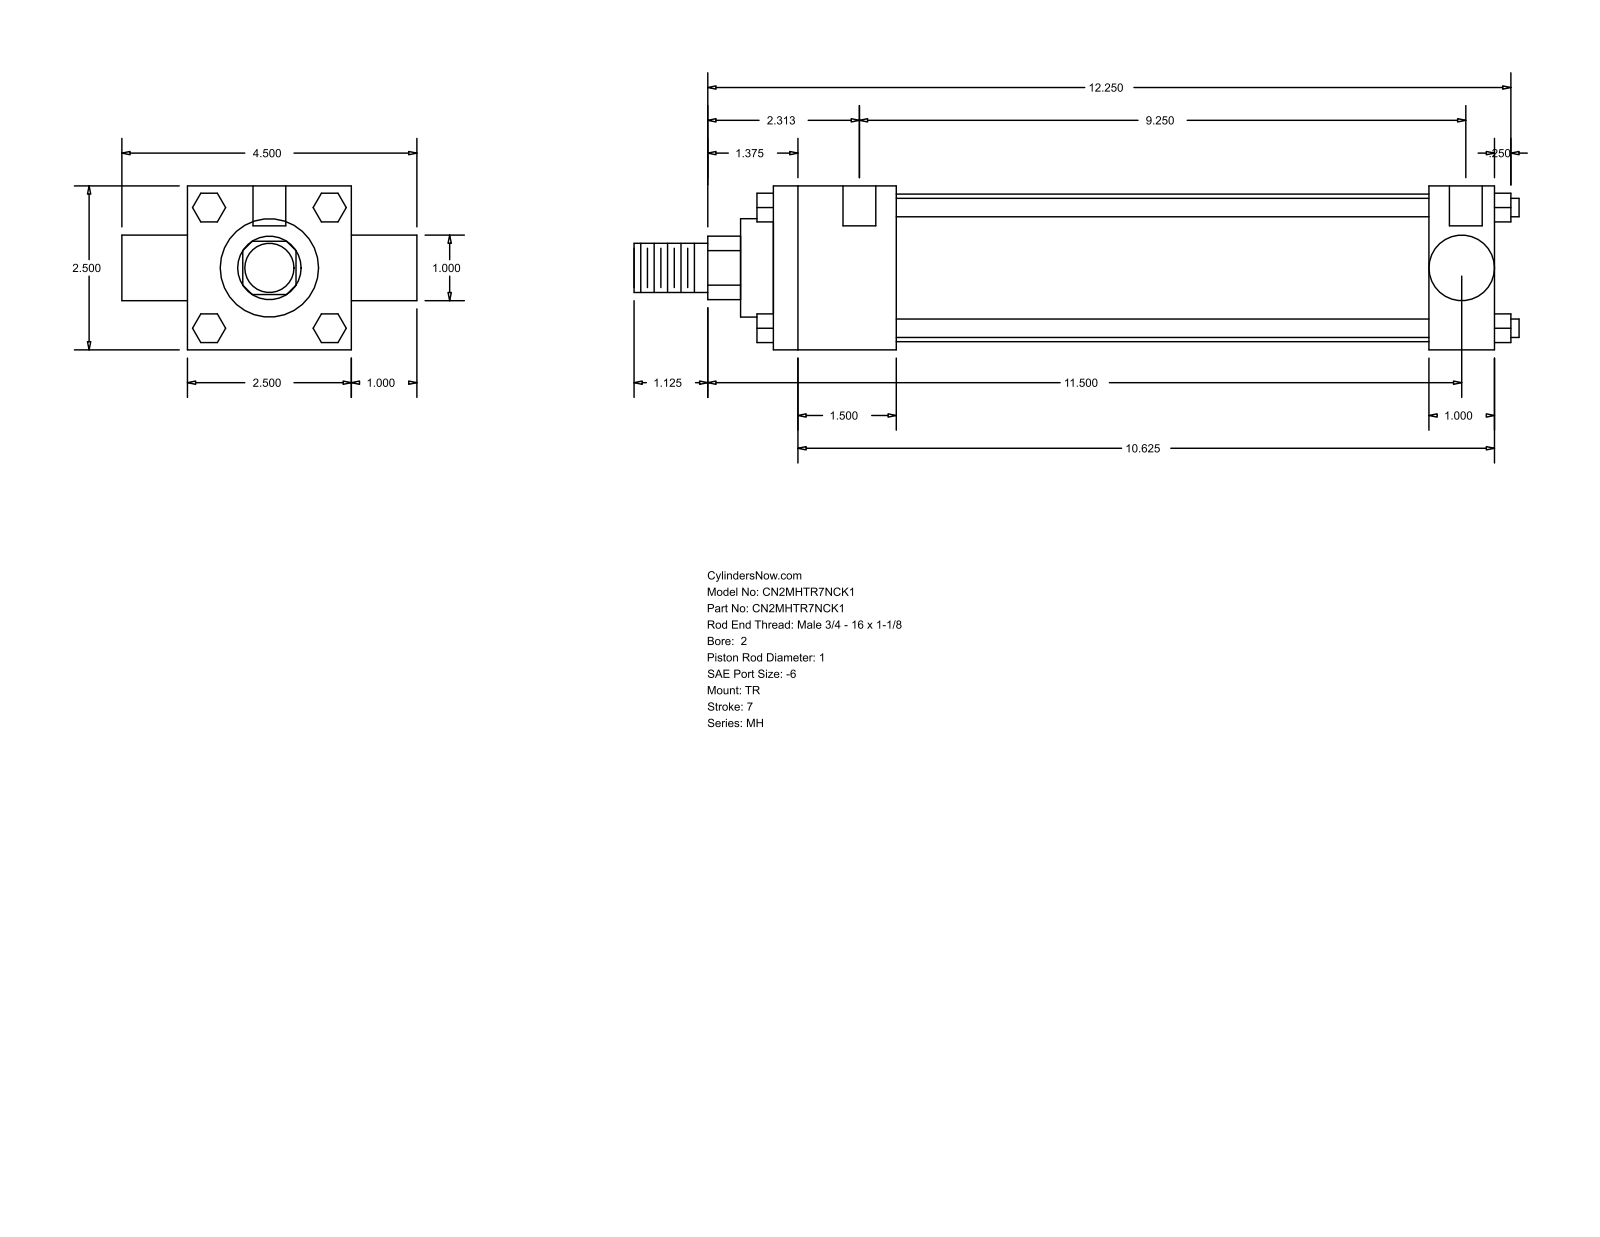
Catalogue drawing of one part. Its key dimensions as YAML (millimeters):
part_name: "MH_TR__0200_1"
step_written_by: "GSSL Pune (CONFIG_CONTROL_DESIGN)"
units: millimeters
bodies: {solids: 0, faces: 120, planar: 92, cylindrical: 28, other: 0}
overall_size: [342.9, 114.3, 63.5]
round_holes:
  - {diameter: 5.56, count: 3}
  - {diameter: 12.7, count: 2}
round_bosses_or_shafts:
  - {diameter: 7.14, count: 4}
  - {diameter: 57.15, count: 1}
  - {diameter: 38.1, count: 1}
  - {diameter: 25.4, count: 1}
  - {diameter: 25.35, count: 1}
  - {diameter: 19.05, count: 1}
partial_cylinders:
  - {radius: 12.29, count: 1}
face_to_face_distances: [63.5, 279.4, 25.4, 47.63, 254, 206.37, 231.77, 88.9, 292.1, 6.35]
hole_center_spacings: [3.17, 4.76, 234.95, 238.12, 239.71, 242.88]
